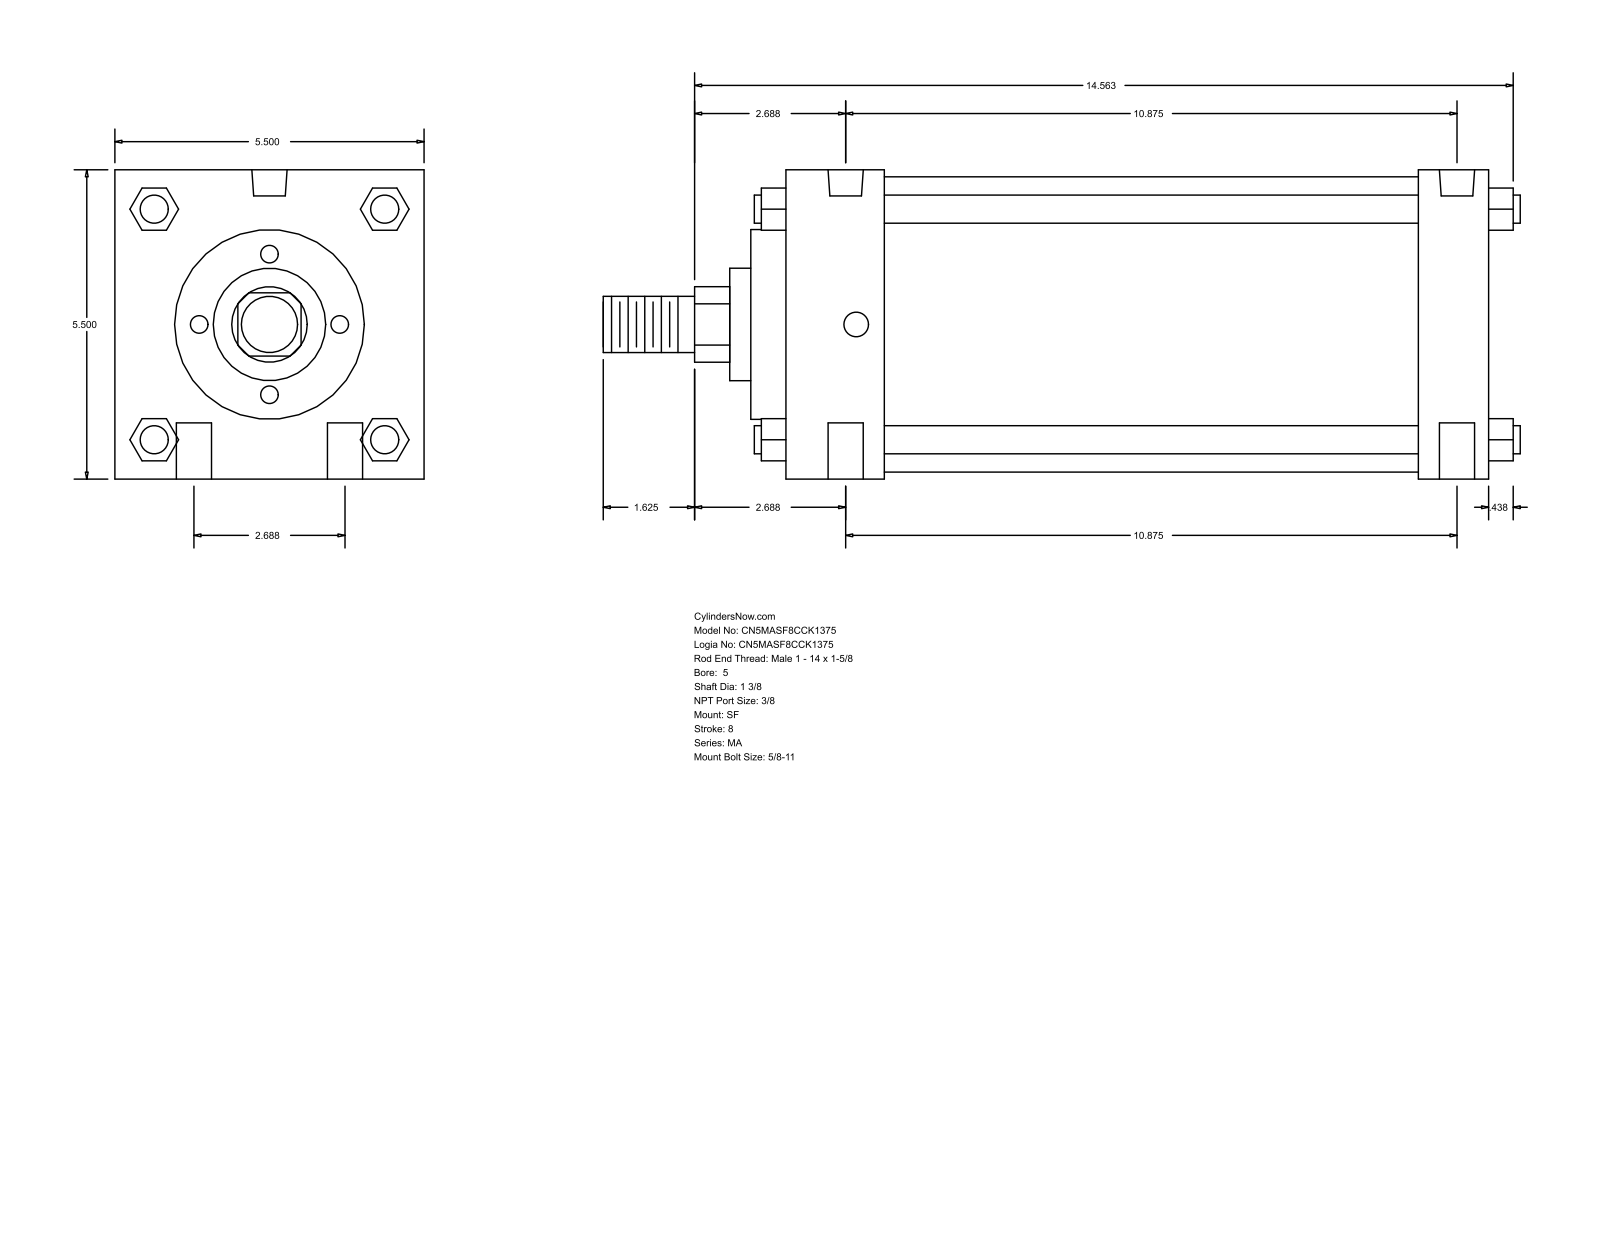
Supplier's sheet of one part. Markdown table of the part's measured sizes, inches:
| quantity | value |
| --- | --- |
| part name | MA_SF__0500_1.375 |
| STEP written by | GSSL Pune (CONFIG_CONTROL_DESIGN) |
| units | inches |
| bodies | 0 solids, 126 faces (95 planar, 31 cylindrical, 0 other) |
| overall size | 16.313 × 5.5 × 5.5 |
| round holes (diameter × count) | 0.625 × 4, 0.437 × 2, 0.627 × 2 |
| round bosses / shafts (diameter × count) | 0.5 × 4, 5.25 × 1, 3.375 × 1, 2 × 1, 1.375 × 1, 1 × 1 |
| partial cylindrical surfaces (radius × count) | 0.672 × 1 |
| main face-to-face distances | 5.5, 12.5, 1.75, 11.25, 9.5, 10.75, 1.25, 0.625, 2.375, 11.875 |
| hole center spacings | 1.344, 10.958, 10.875, 2.687, 11.202, 10.5 |
